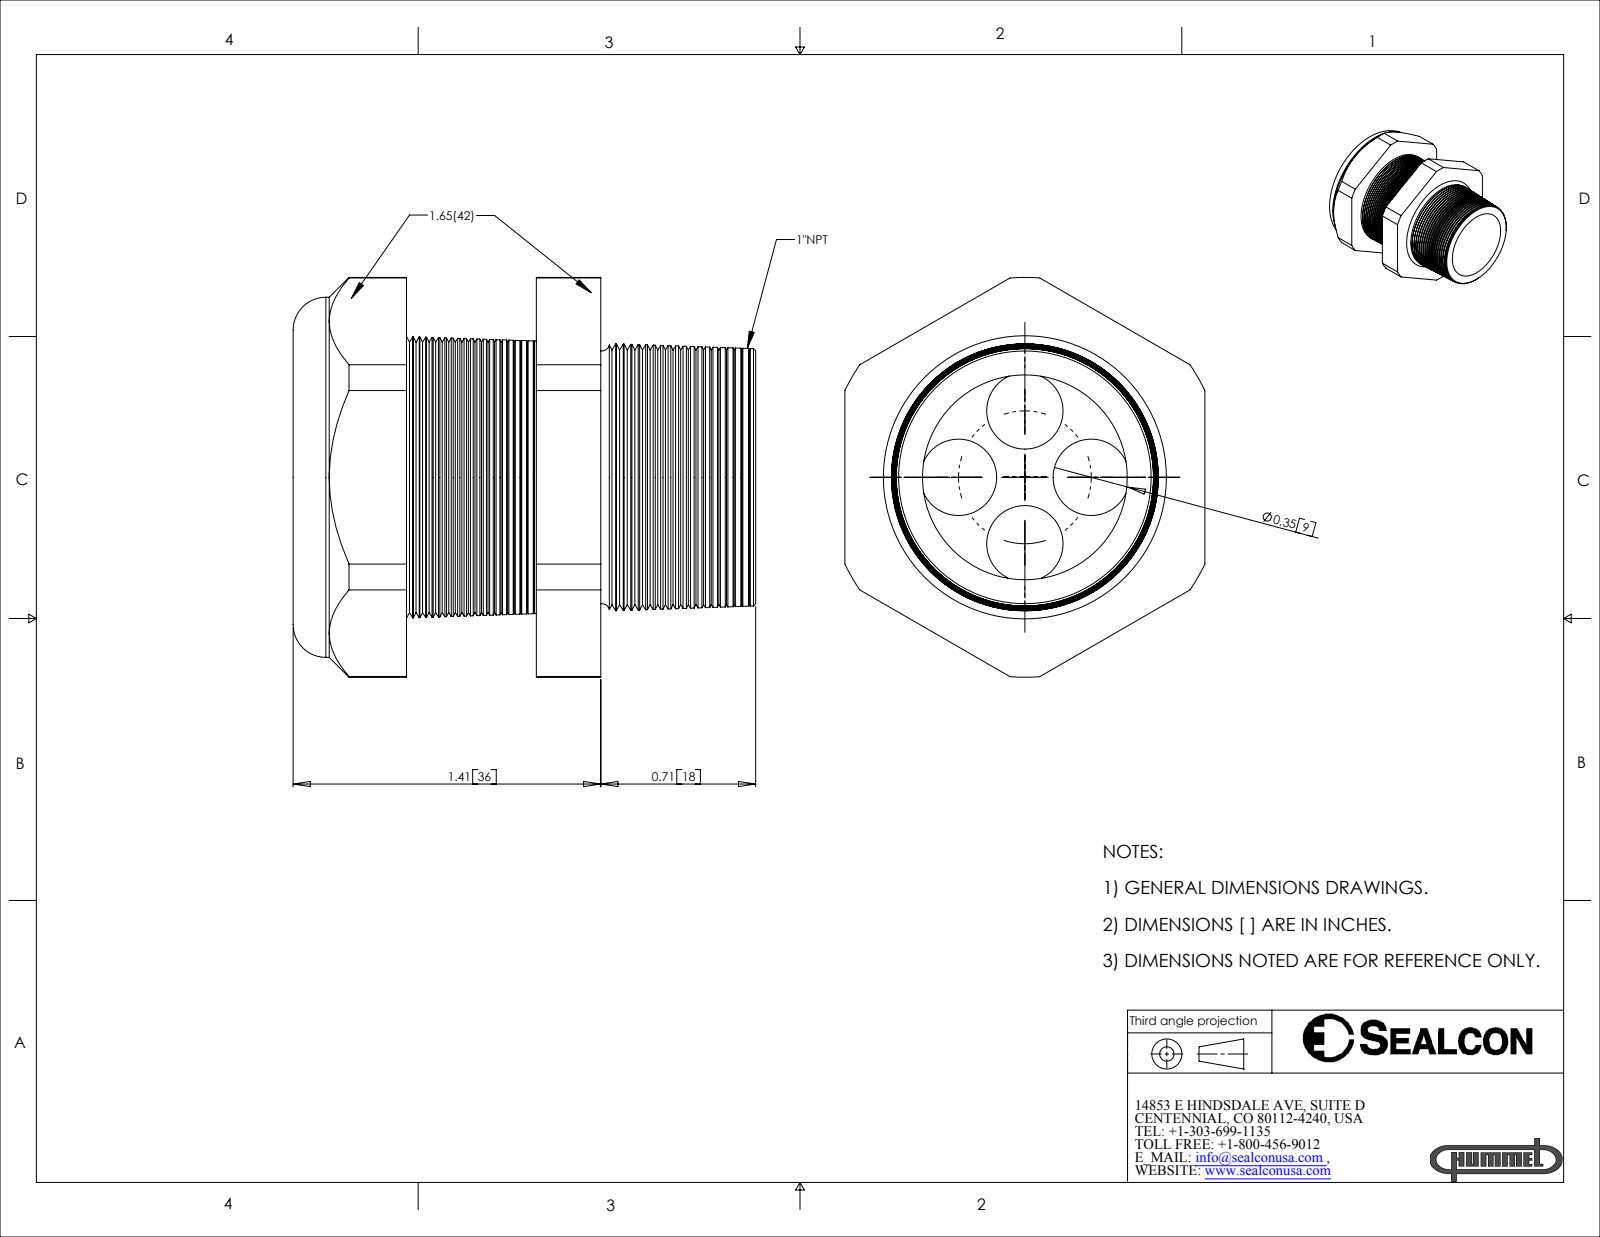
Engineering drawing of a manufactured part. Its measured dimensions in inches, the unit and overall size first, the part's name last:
Units: inches
Overall size (bounding box): 2.12 × 1.831 × 1.65
Round holes (diameter × count): ⌀0.35 ×4, ⌀0.96 ×1, ⌀0.98 ×1
Round bosses / shafts (diameter × count): ⌀1.65 ×1
Partial cylindrical surfaces — rounded edges, fillets, slot ends (radius × count): R0.916 ×1
Main face-to-face distances: 0.555, 0.85, 0.295, 1.65, 0.52, 1.075, 1.37, 1.65, 0.5, 0.02
Hole centre spacings: 0.304, 0.43, 0.609
Volume: 1.995 in³ · Surface area: 28.34 in²
Bodies: 2 solids, 298 faces (20 planar, 28 cylindrical, 250 other)
Part name (STEP PRODUCT): CD29N2-GY
STEP written by: SolidWorks 2007 (CONFIG_CONTROL_DESIGN)
